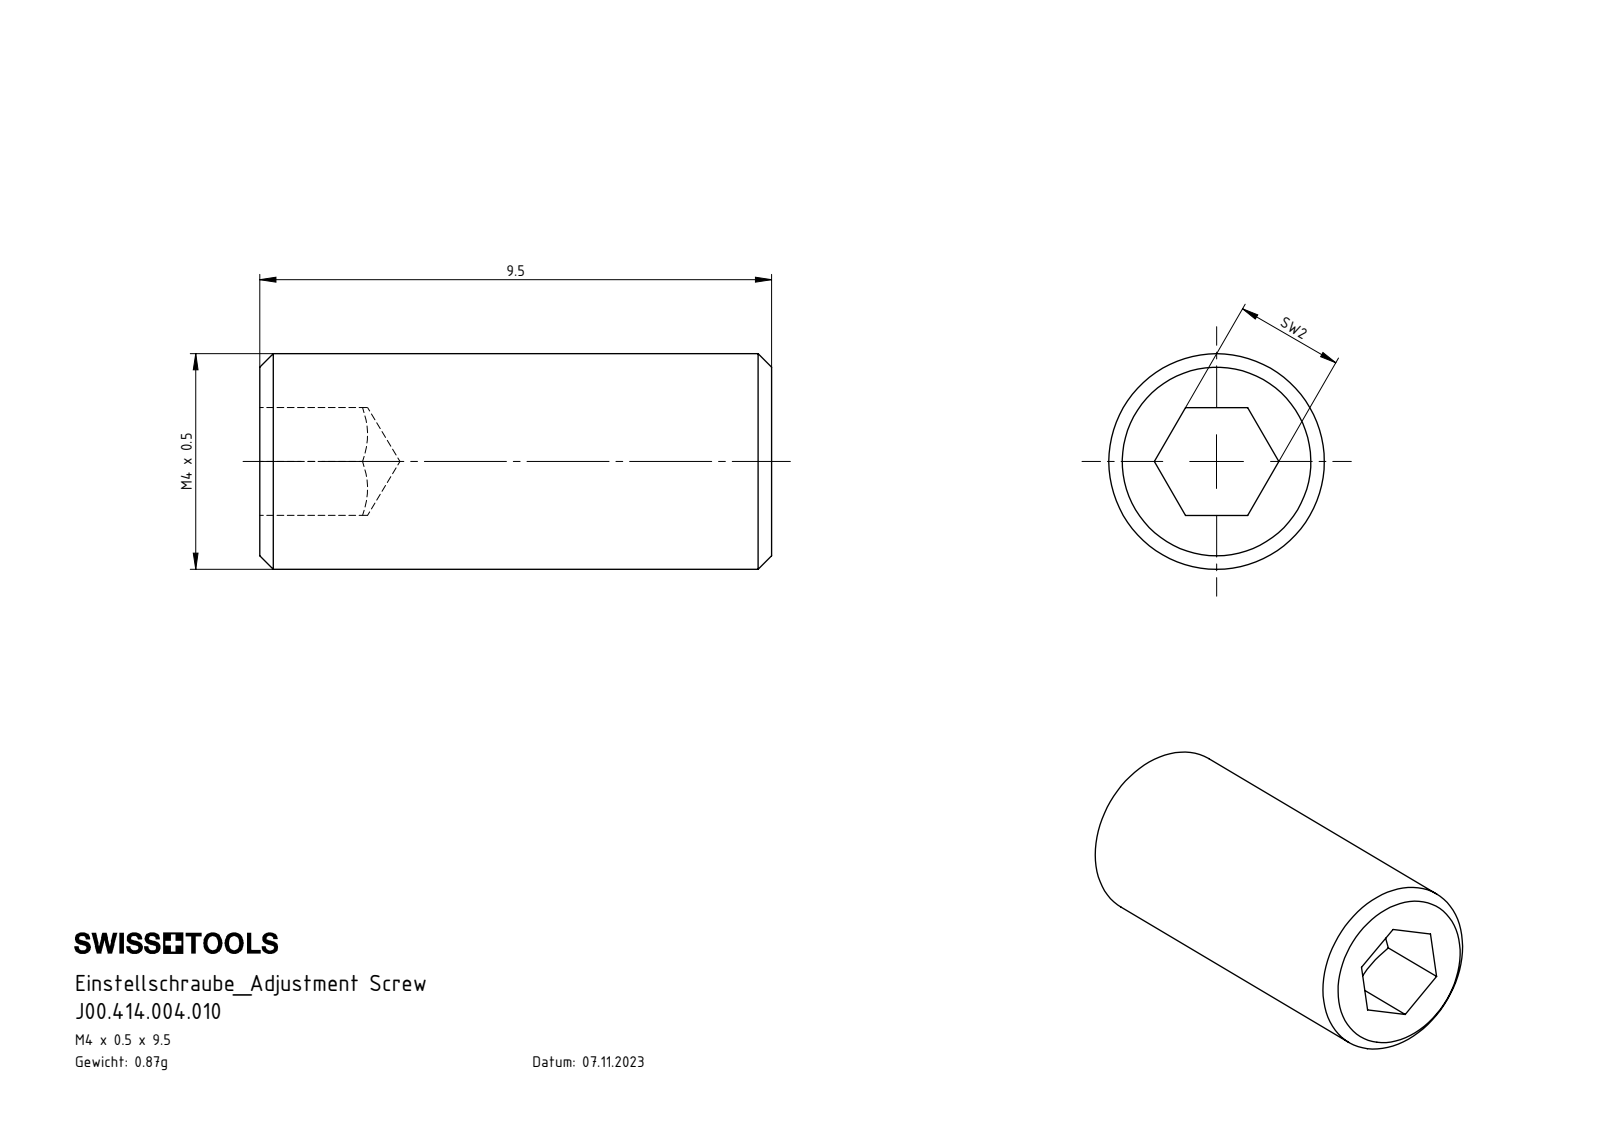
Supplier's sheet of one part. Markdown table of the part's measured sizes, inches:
| quantity | value |
| --- | --- |
| part name | J00.414.004.010 |
| STEP written by | SolidWorks 2022 (AUTOMOTIVE_DESIGN) |
| units | inches |
| bodies | 1 solid, 16 faces (8 planar, 2 cylindrical, 6 other) |
| overall size | 0.374 × 0.157 × 0.157 |
| volume | 0.007 in³ |
| surface area | 0.24 in² |
| round bosses / shafts (diameter × count) | 0.157 × 1 |
| main face-to-face distances | 0.079, 0.374 |
